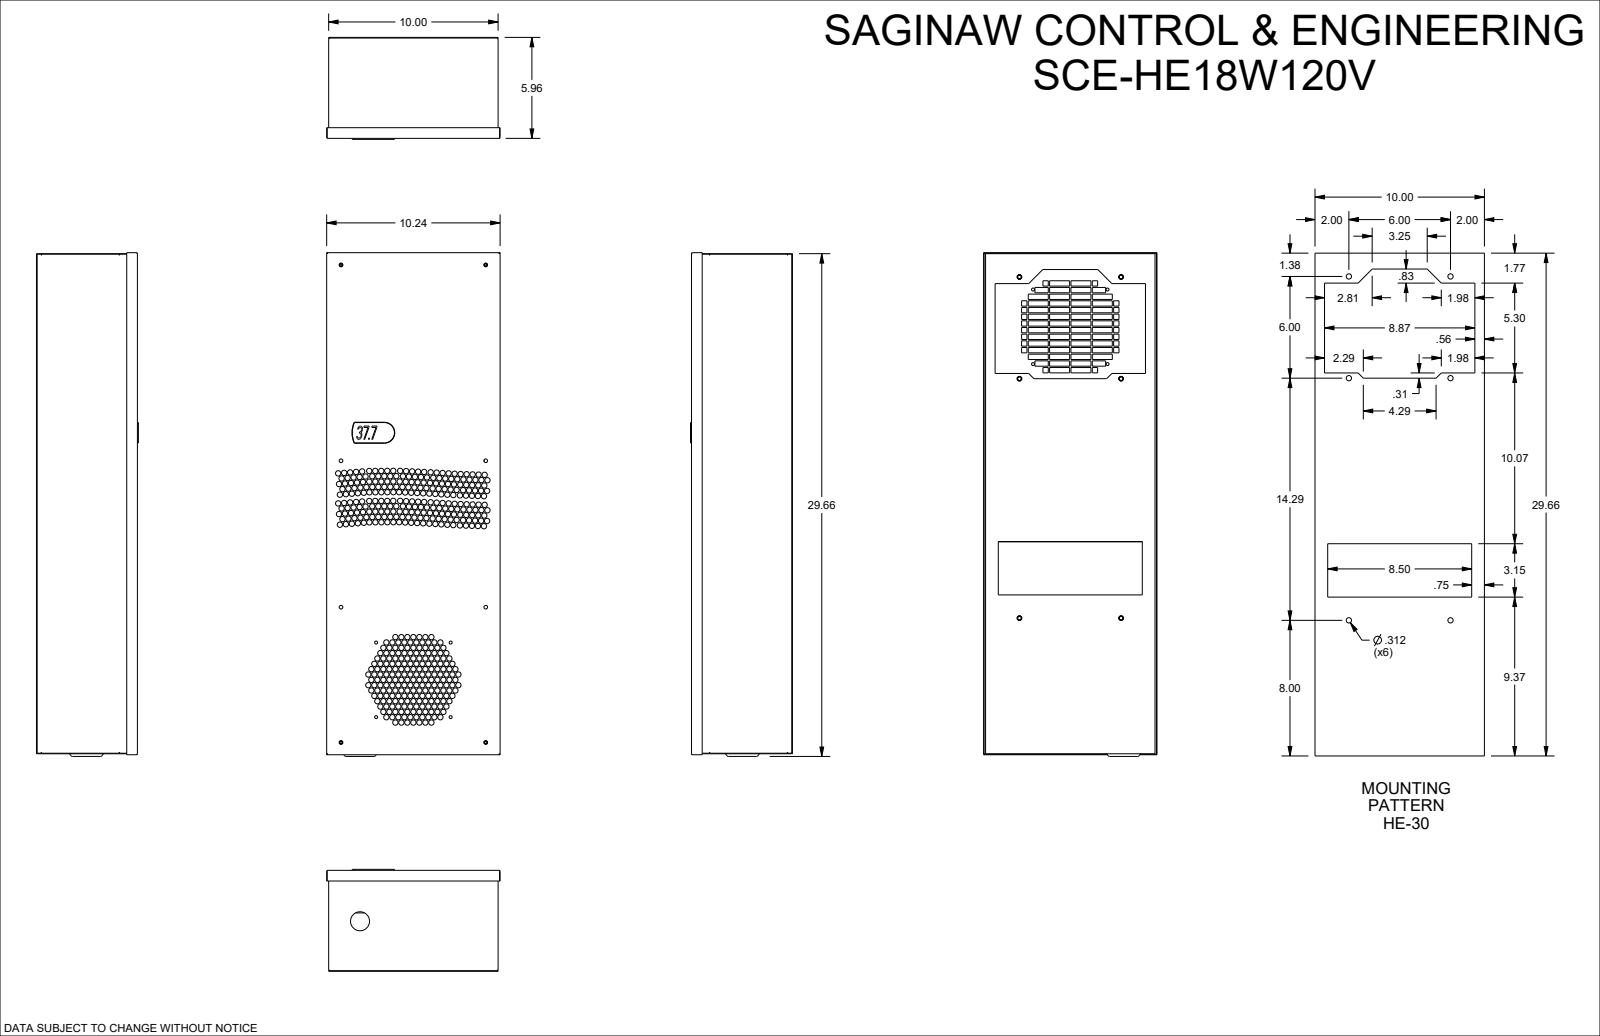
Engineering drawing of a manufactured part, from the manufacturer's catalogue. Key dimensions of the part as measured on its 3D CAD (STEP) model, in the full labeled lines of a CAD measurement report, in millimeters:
Part name (STEP PRODUCT): SCE-HE18W120V
STEP written by: SolidWorks 2023 (AUTOMOTIVE_DESIGN)
Units: millimetres
Bodies: 1 solid, 1377 faces (881 planar, 493 cylindrical, 3 other)
Overall size (bounding box): 754.8 × 260 × 154.6
Volume: 28 820 000 mm³ · Surface area: 709 000 mm²
Round holes (diameter × count): ⌀8 ×461, ⌀4.5 ×8, ⌀5.5 ×8, ⌀7 ×6, ⌀16.5 ×1, ⌀28.5 ×1
Partial cylindrical surfaces — rounded edges, fillets, slot ends (radius × count): R1.6 ×4, R15.2 ×1, R15.7 ×1, R37.5 ×1, R38 ×1
Main face-to-face distances: 151.3, 254, 0.8, 150.5, 149.7, 749.3, 3, 257, 1.6, 148.9
Hole centre spacings: 16, 18.4, 33.2, 9, 32, 89.8, 48.8, 79.2
